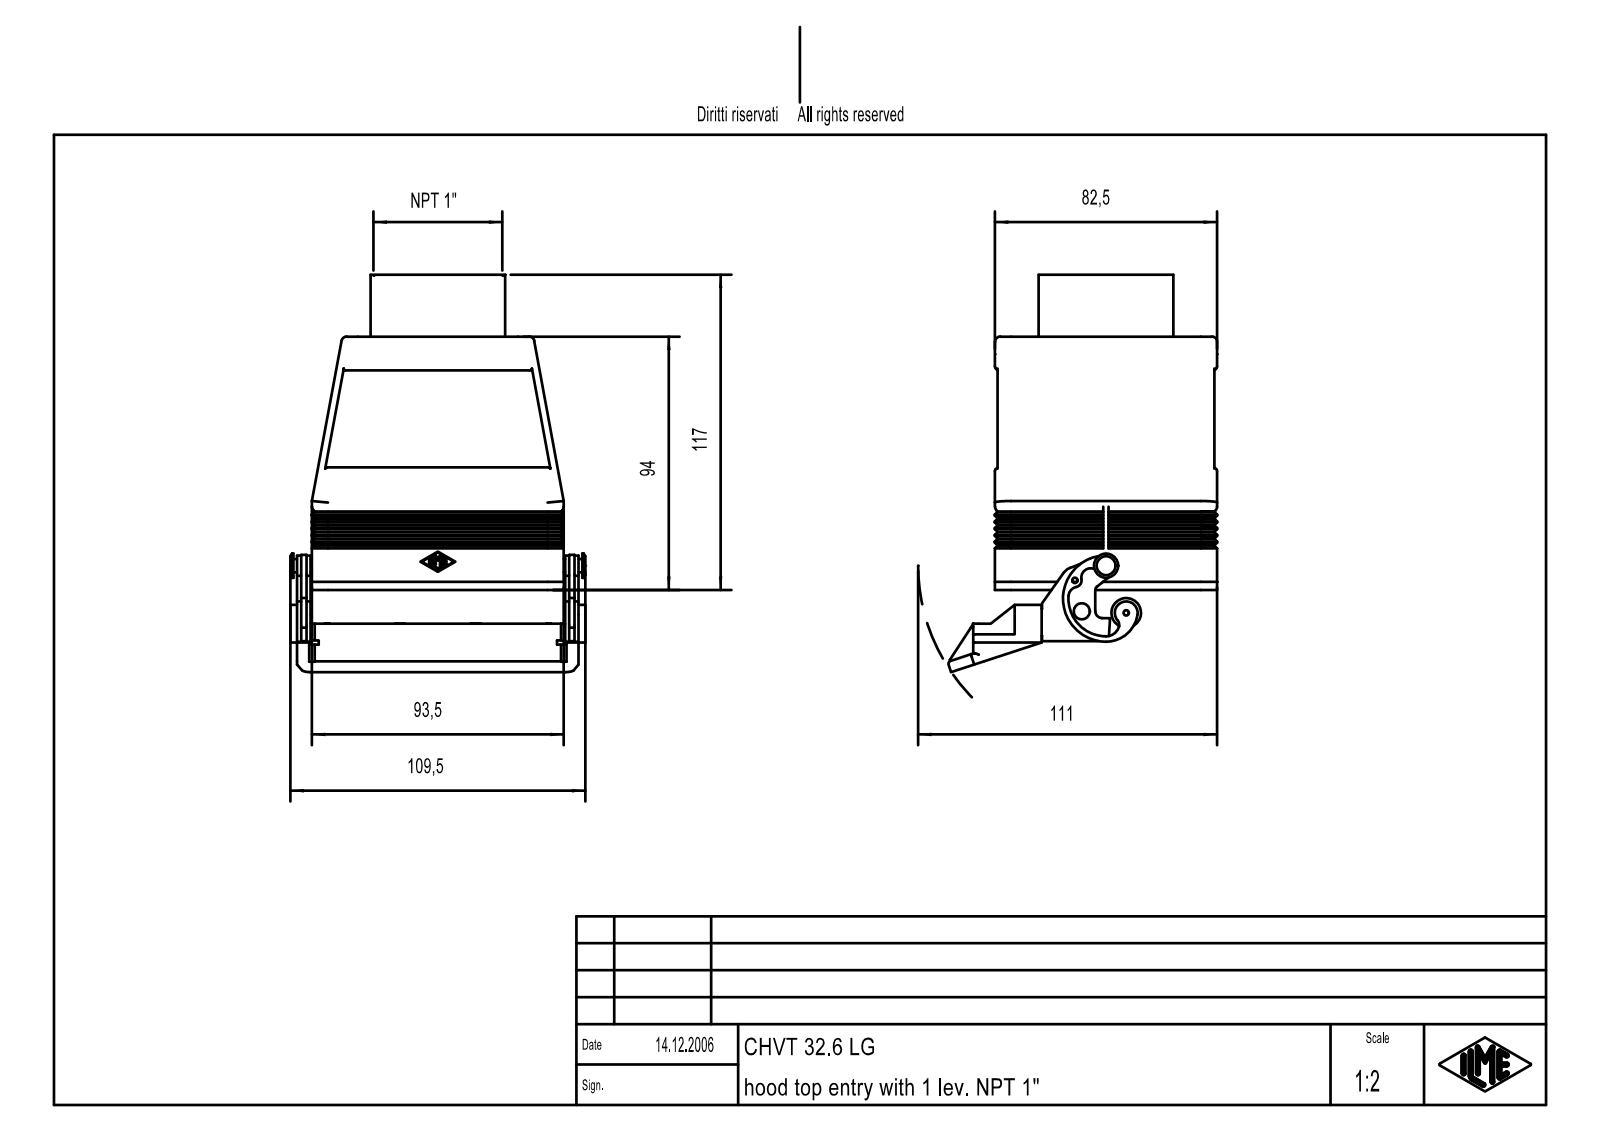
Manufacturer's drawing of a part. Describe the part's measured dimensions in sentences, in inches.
The part is named "p1; p2; p3; p4 (+3 more)". Its 3-D file was written by "Creo Elements/Direct Modeling 18.0B 02-Dec-2011 (C) Parametric Technology GmbH (AUTOMOTIVE_DESIGN)". It is 5 solids with 715 faces: 388 planar, 239 cylindrical and 88 other. Overall it measures 5.806 by 4.311 by 3.926 inches. Its volume is 13.32 cubic inches and its surface area 147 square inches. Round holes: 8 of diameter 0.097, 8 of diameter 0.138, 2 of diameter 0.079, 1 of diameter 0.098, 1 of diameter 0.236. Round bosses or shafts: 1 of diameter 2.362, 1 of diameter 1.969, 1 of diameter 0.433, 1 of diameter 0.354, 1 of diameter 0.197. Partial cylindrical surfaces (rounded edges, fillets, slot ends): 20 of radius 0.079, 14 of radius 0.01, 12 of radius 0.236, 9 of radius 0.039, 6 of radius 0.118, 6 of radius 0.197, 4 of radius 0.13, 3 of radius 0.098. The main face-to-face distances are 0.157, 0.039, 0.118, 2.933, 3.051, 3.091, 3.209, 3.248, 0.315, 3.366. The hole center spacings are 1.063, 1.358, 3.051, 3.231, 3.34, 0.295, 2.421, 3.065.
